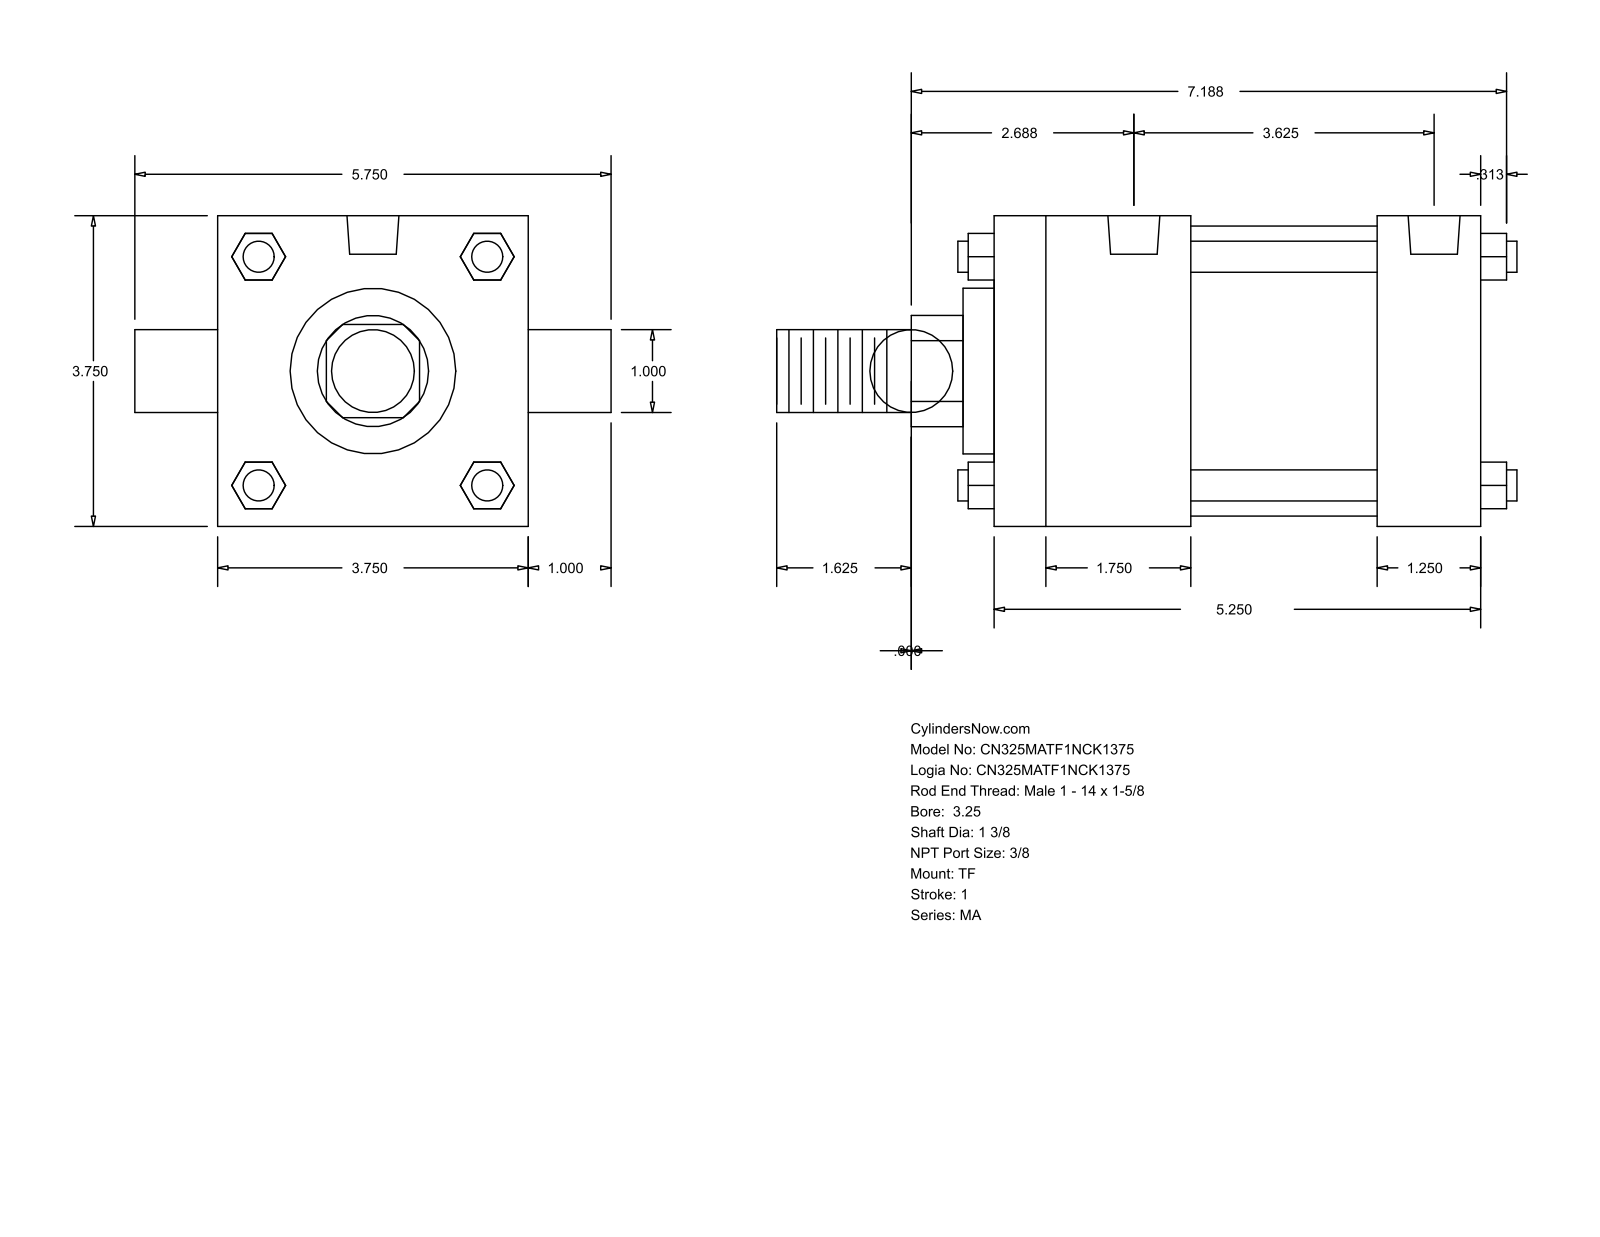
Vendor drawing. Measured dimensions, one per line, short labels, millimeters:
name: MA_TF__0325_1.375
written by: GSSL Pune (CONFIG_CONTROL_DESIGN)
unit: mm
bodies: 0 solids, 120 faces (92 planar, 28 cylindrical, 0 other)
size: 227.01 × 146.05 × 95.25
holes: 3× ⌀11.11, 2× ⌀15.93
bosses: 4× ⌀9.53, 2× ⌀25.4, 1× ⌀88.9, 1× ⌀50.8, 1× ⌀34.92
rounds: 1× R17.06
face distances: 95.24, 149.22, 60.32, 117.48, 57.16, 88.9, 31.74, 9.52, 69.84, 127
hole spacings: 4.77, 87.31, 82.54, 92.08
